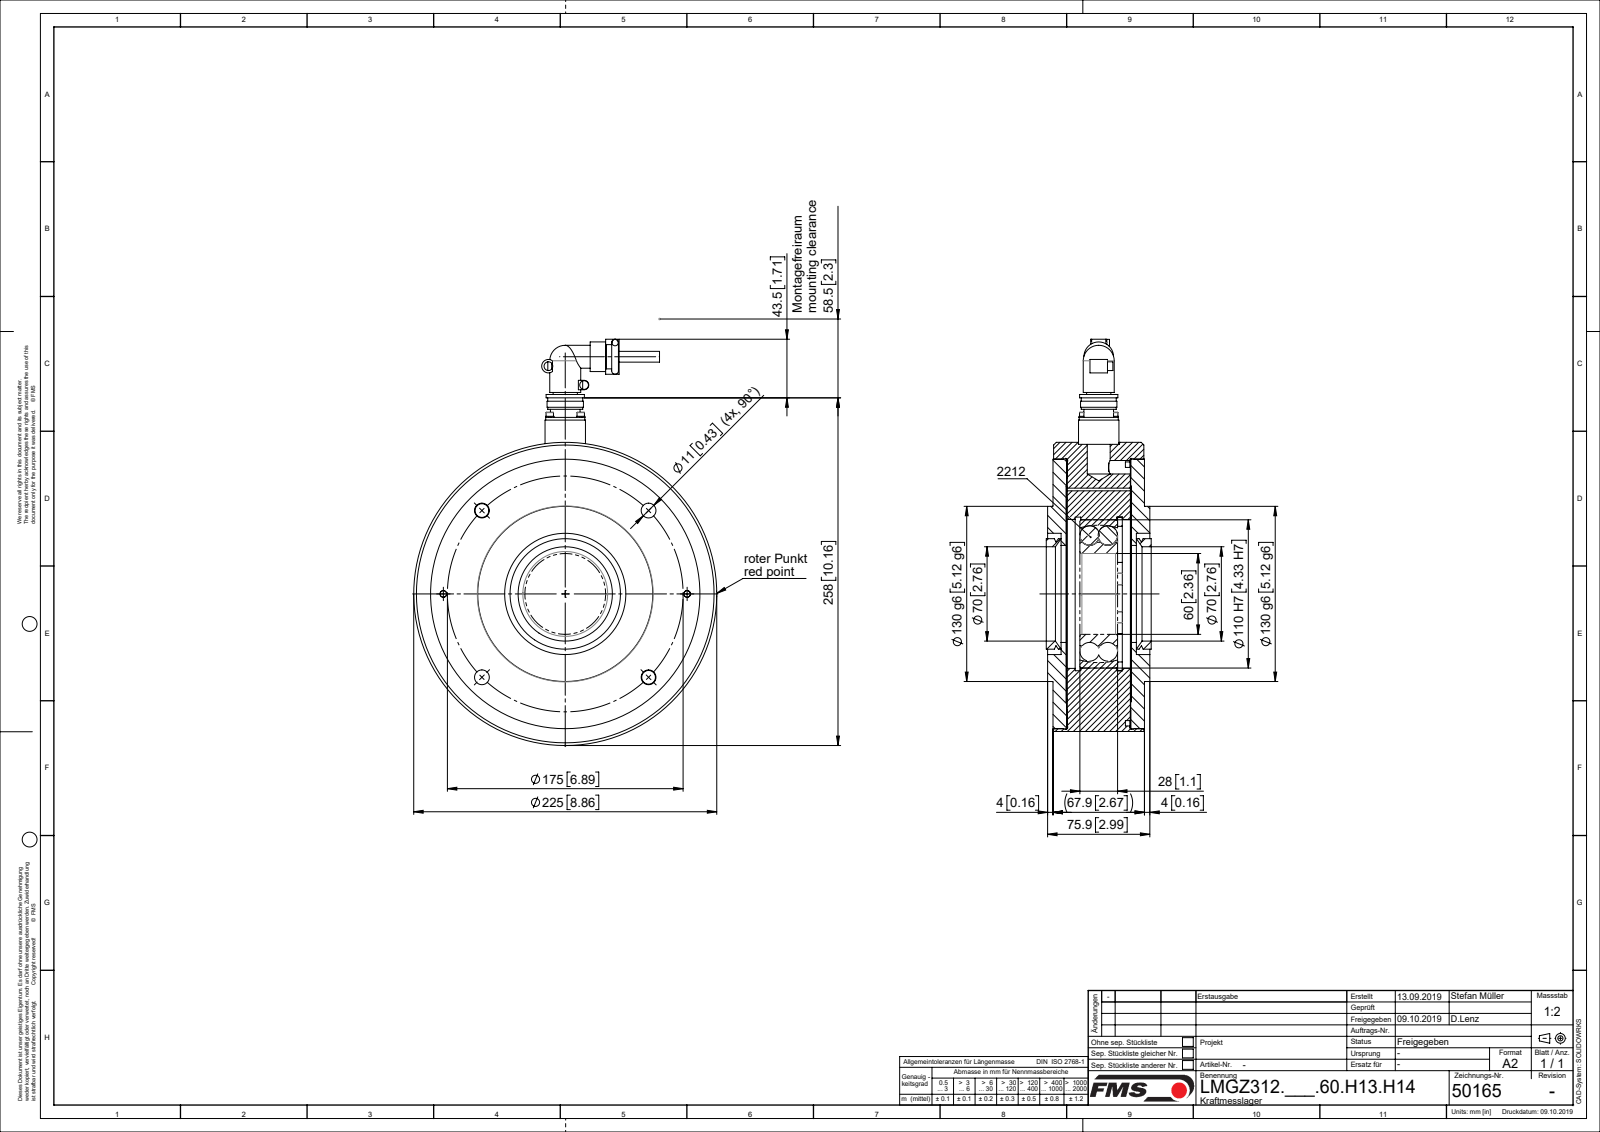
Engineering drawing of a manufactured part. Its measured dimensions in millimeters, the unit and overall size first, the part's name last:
Units: millimetres
Overall size (bounding box): 301.5 × 225 × 77.9
Round holes (diameter × count): ⌀11 ×6, ⌀2.6 ×4, ⌀3.2 ×4, ⌀3.4 ×4, ⌀3.5 ×4, ⌀9 ×4, ⌀5 ×2, ⌀6.6 ×2, ⌀23 ×1, ⌀60 ×1, ⌀70 ×1, ⌀72 ×1
Round bosses / shafts (diameter × count): ⌀6.2 ×4, ⌀5.5 ×4, ⌀3 ×4, ⌀22 ×2, ⌀10 ×2, ⌀6.5 ×2, ⌀6 ×2, ⌀4.8 ×2
Partial cylindrical surfaces — rounded edges, fillets, slot ends (radius × count): R2.5 ×2, R3.5 ×1, R5 ×1, R81 ×1, R86 ×1
Main face-to-face distances: 47.25, 10.45, 10.2, 57.45, 57.7, 47.5, 0.5, 48, 9.7, 58.2
Hole centre spacings: 16.26, 23, 68.17, 87.5, 123.74, 164.45, 32.53, 90.5
Volume: 2 386 000 mm³ · Surface area: 395 980 mm²
Bodies: 21 solids, 424 faces (123 planar, 238 cylindrical, 63 other)
Part name (STEP PRODUCT): L50165; L4765504; TEIL1; L49026 (+8 more)
STEP written by: Mechanical Desktop 2007 (CONFIG_CONTROL_DESIGN)
